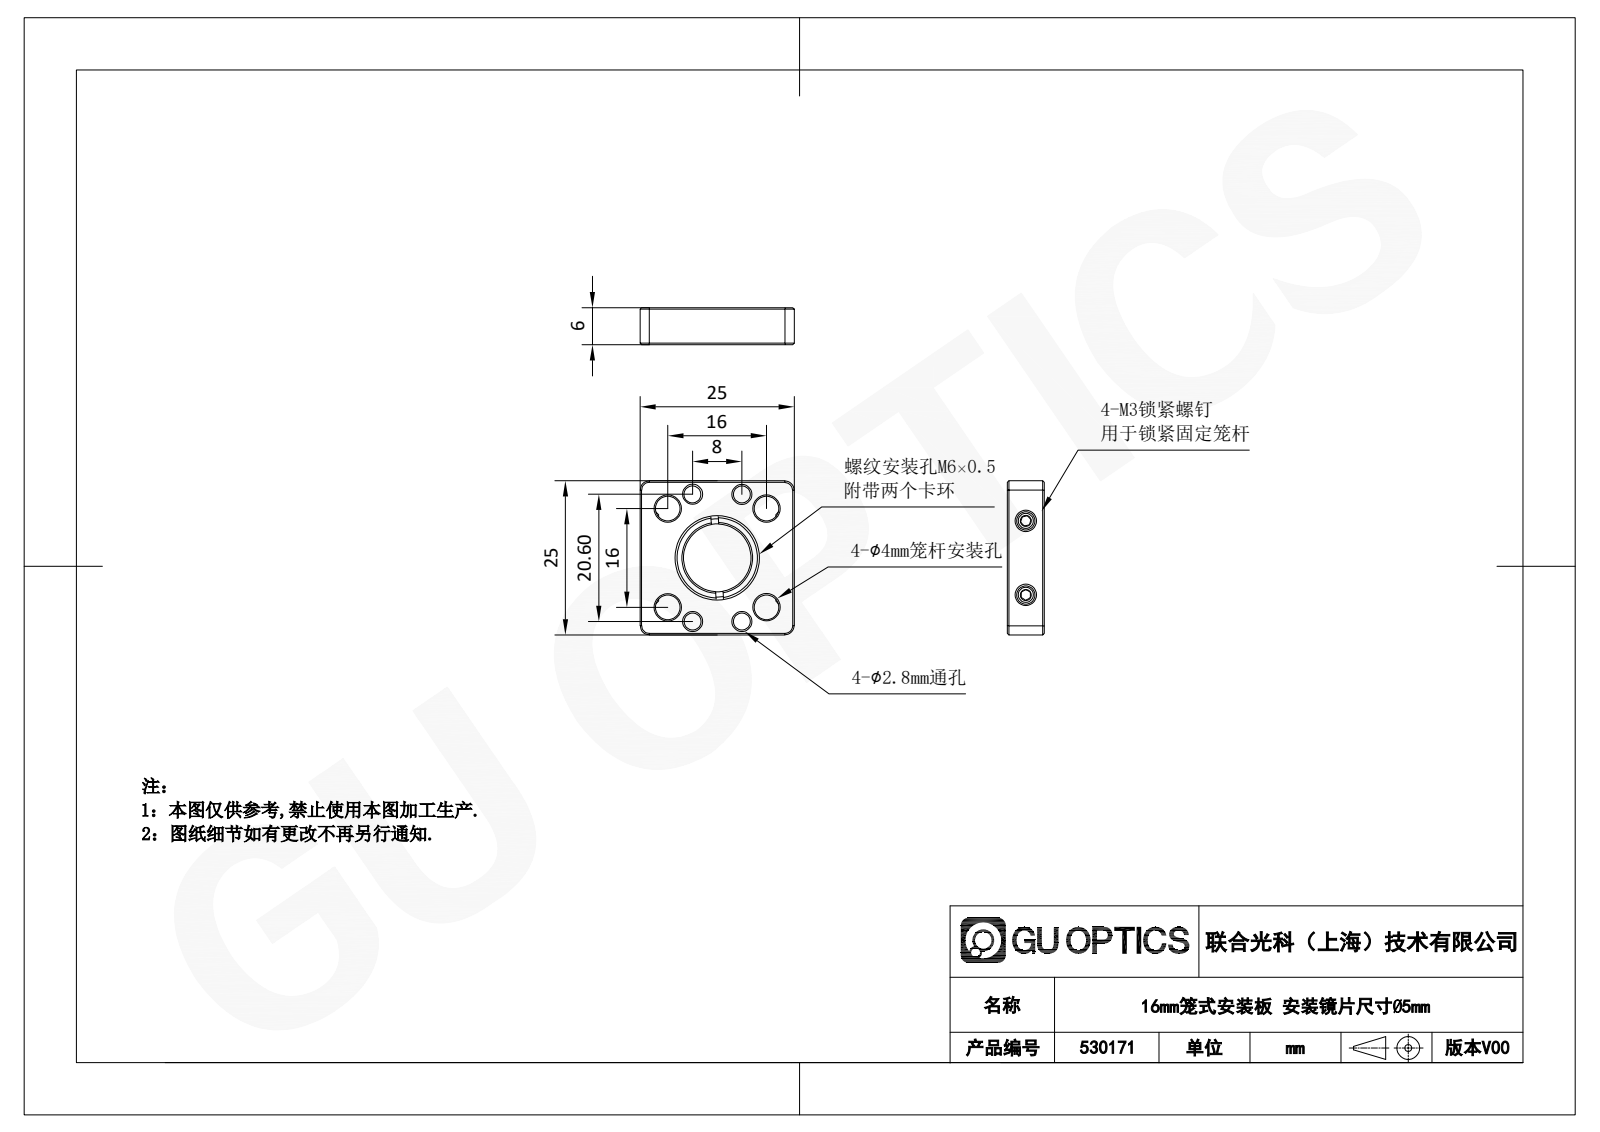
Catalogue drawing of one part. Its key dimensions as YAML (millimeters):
part_name: "530171"
step_written_by: "SolidWorks 2020 (CONFIG_CONTROL_DESIGN)"
units: millimeters
bodies: {solids: 7, faces: 276, planar: 138, cylindrical: 25, other: 113}
overall_size: [25, 25, 6]
volume: 3179
surface_area: 2620
round_holes:
  - {diameter: 2.8, count: 4}
  - {diameter: 4, count: 4}
  - {diameter: 2.5, count: 2}
  - {diameter: 3.5, count: 1}
  - {diameter: 5.5, count: 1}
round_bosses_or_shafts:
  - {diameter: 3, count: 2}
  - {diameter: 6, count: 1}
partial_cylinders:
  - {radius: 1.5, count: 4}
face_to_face_distances: [6, 25, 2, 21.56, 4, 3, 22, 1.5, 1, 24]
hole_center_spacings: [4.61, 11.05, 11.31, 12.22, 16, 18.73, 21.88, 8]
